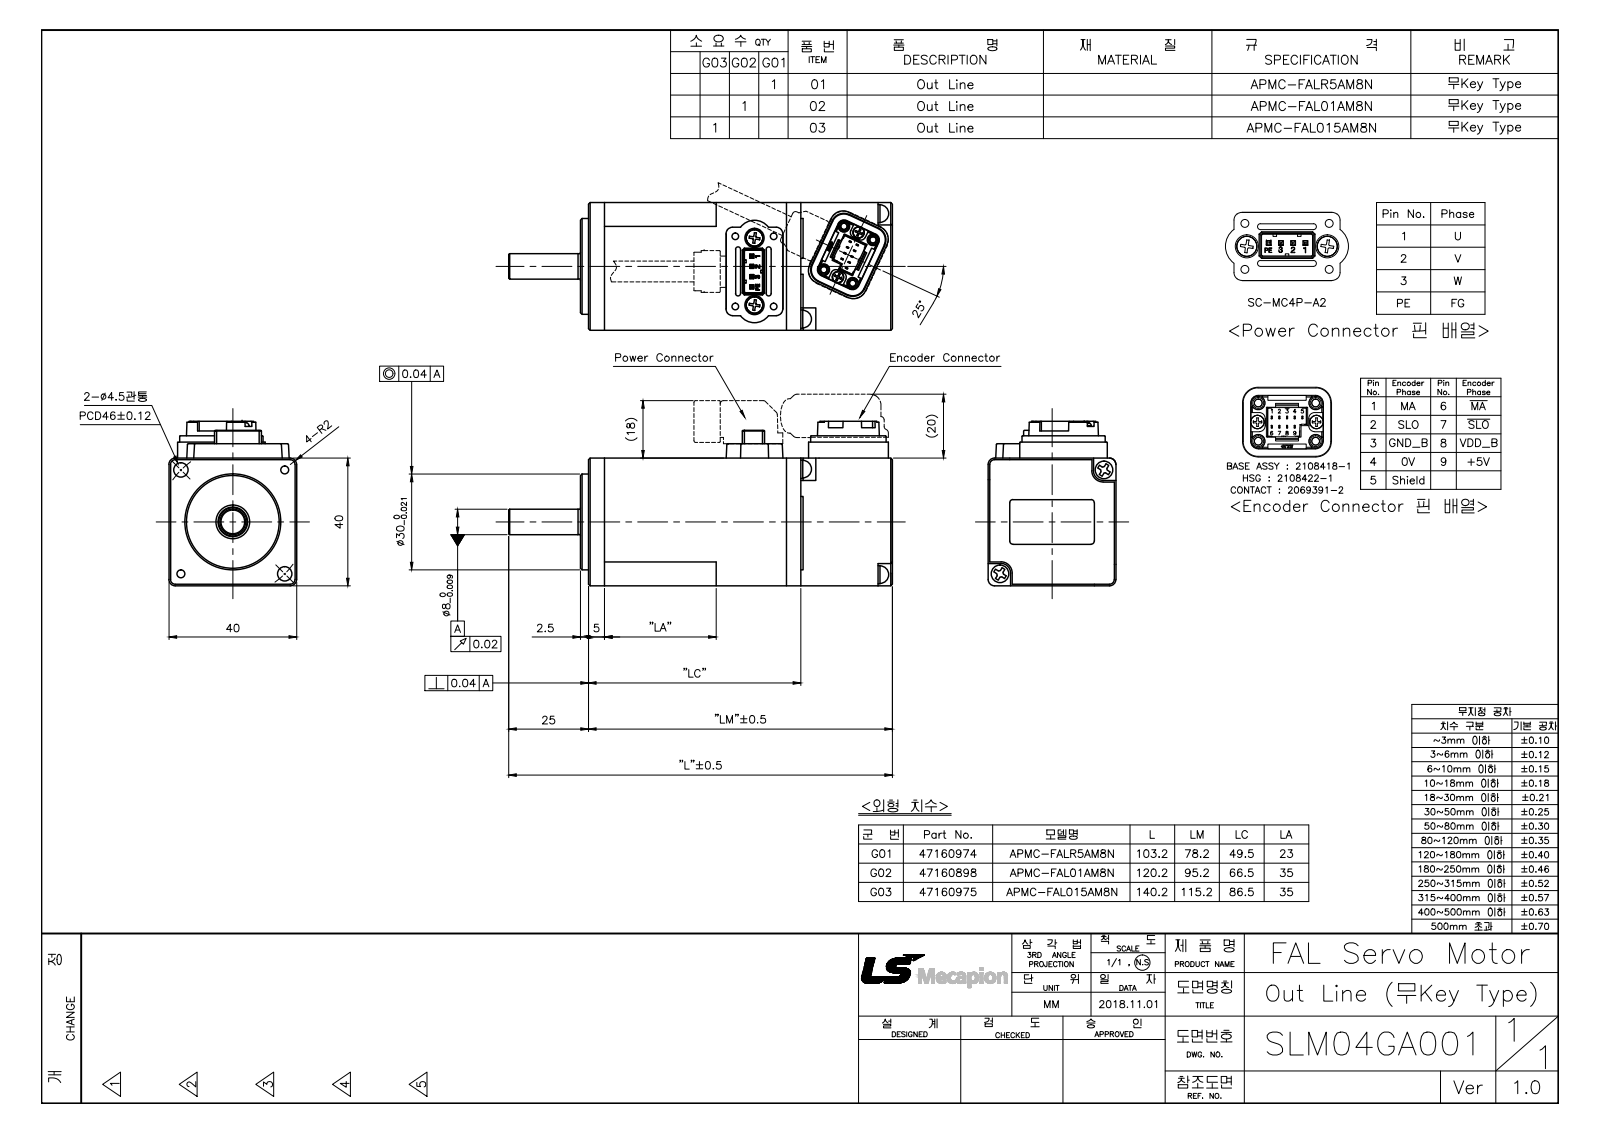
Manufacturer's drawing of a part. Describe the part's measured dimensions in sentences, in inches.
The part is named "APMC-FAL015AM8N". Its 3-D file was written by "SolidWorks 2011 (AUTOMOTIVE_DESIGN)". It is 28 solids with 1359 faces: 906 planar, 287 cylindrical and 166 other. Overall it measures 5.52 by 2.028 by 1.575 inches. Its volume is 11.43 cubic inches and its surface area 72.22 square inches. Round holes: 10 of diameter 0.083, 6 of diameter 0.118, 4 of diameter 0.142, 2 of diameter 0.079, 2 of diameter 0.087, 2 of diameter 0.098, 2 of diameter 0.177, 2 of diameter 0.236, 1 of diameter 0.13, 1 of diameter 0.134, 1 of diameter 0.417. Round bosses or shafts: 6 of diameter 0.213, 1 of diameter 1.181, 1 of diameter 0.386, 1 of diameter 0.315. Partial cylindrical surfaces (rounded edges, fillets, slot ends): 20 of radius 0.008, 9 of radius 0.006, 8 of radius 0.039, 7 of radius 0.018, 6 of radius 0.004, 6 of radius 0.059, 4 of radius 0.012, 4 of radius 0.03. The main face-to-face distances are 1.575, 0.177, 3.209, 3.031, 0.028, 0.205, 3.236, 0.197, 1.13, 0.098. The hole center spacings are 0.237, 0.63, 0.879, 0.906, 1.28, 0.197, 0.197, 0.394.
